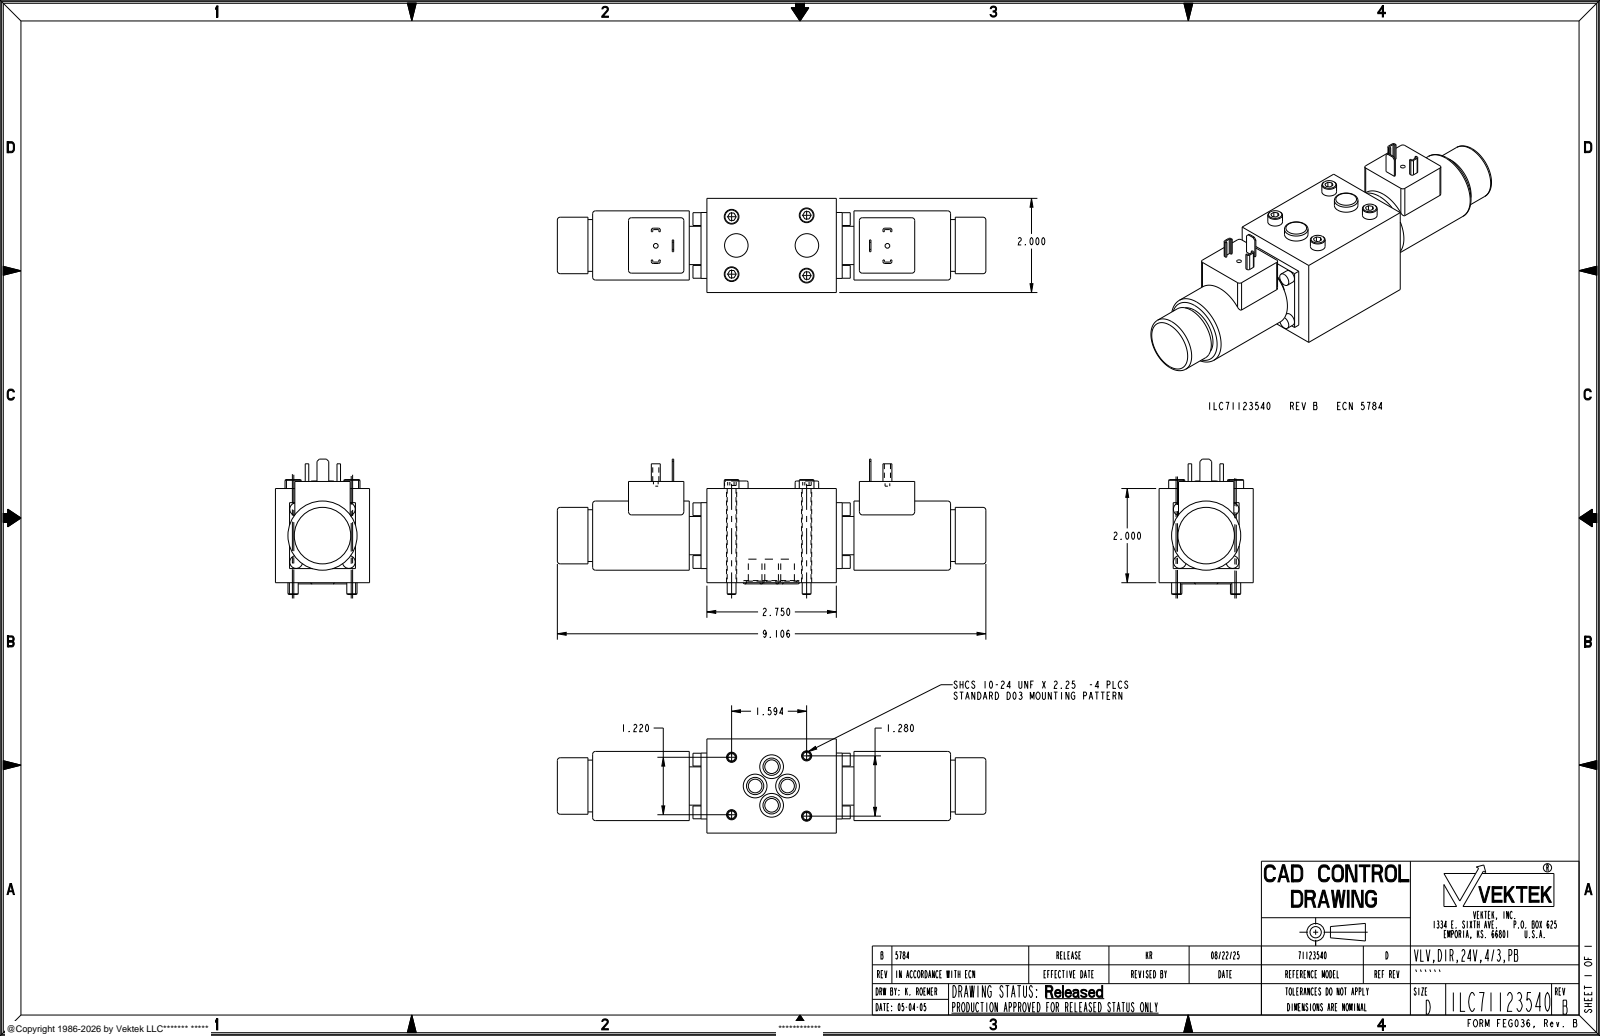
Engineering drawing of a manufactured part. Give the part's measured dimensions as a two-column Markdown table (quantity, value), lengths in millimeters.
| quantity | value |
| --- | --- |
| part name | ILC71123540 |
| STEP written by | CREO PARAMETRIC BY PTC INC, 2021164 (AUTOMOTIVE_DESIGN) |
| units | millimeters |
| bodies | 1 solid, 284 faces (144 planar, 104 cylindrical, 36 other) |
| overall size | 231.3 × 73 × 50.8 |
| volume | 356 900 mm³ |
| surface area | 54 670 mm² |
| round holes (diameter × count) | 5.5 × 4, 7.4 × 4, 12.4 × 4, 2.5 × 2 |
| round bosses / shafts (diameter × count) | 8 × 4, 6.9 × 4, 4.7 × 4, 12.7 × 2, 37.3 × 1, 30.5 × 1, 27.9 × 1, 20.7 × 1 |
| partial cylindrical surfaces (radius × count) | 0.4 × 8, 1 × 8, 1.5 × 8 |
| main face-to-face distances | 50.8, 10.5, 40.3, 54.6, 3.8, 6.4, 3.2, 73, 9.5, 79.4 |
| hole center spacings | 13.5, 13.7, 19.2, 19.8, 20, 22.2, 32.2, 32.7 |
